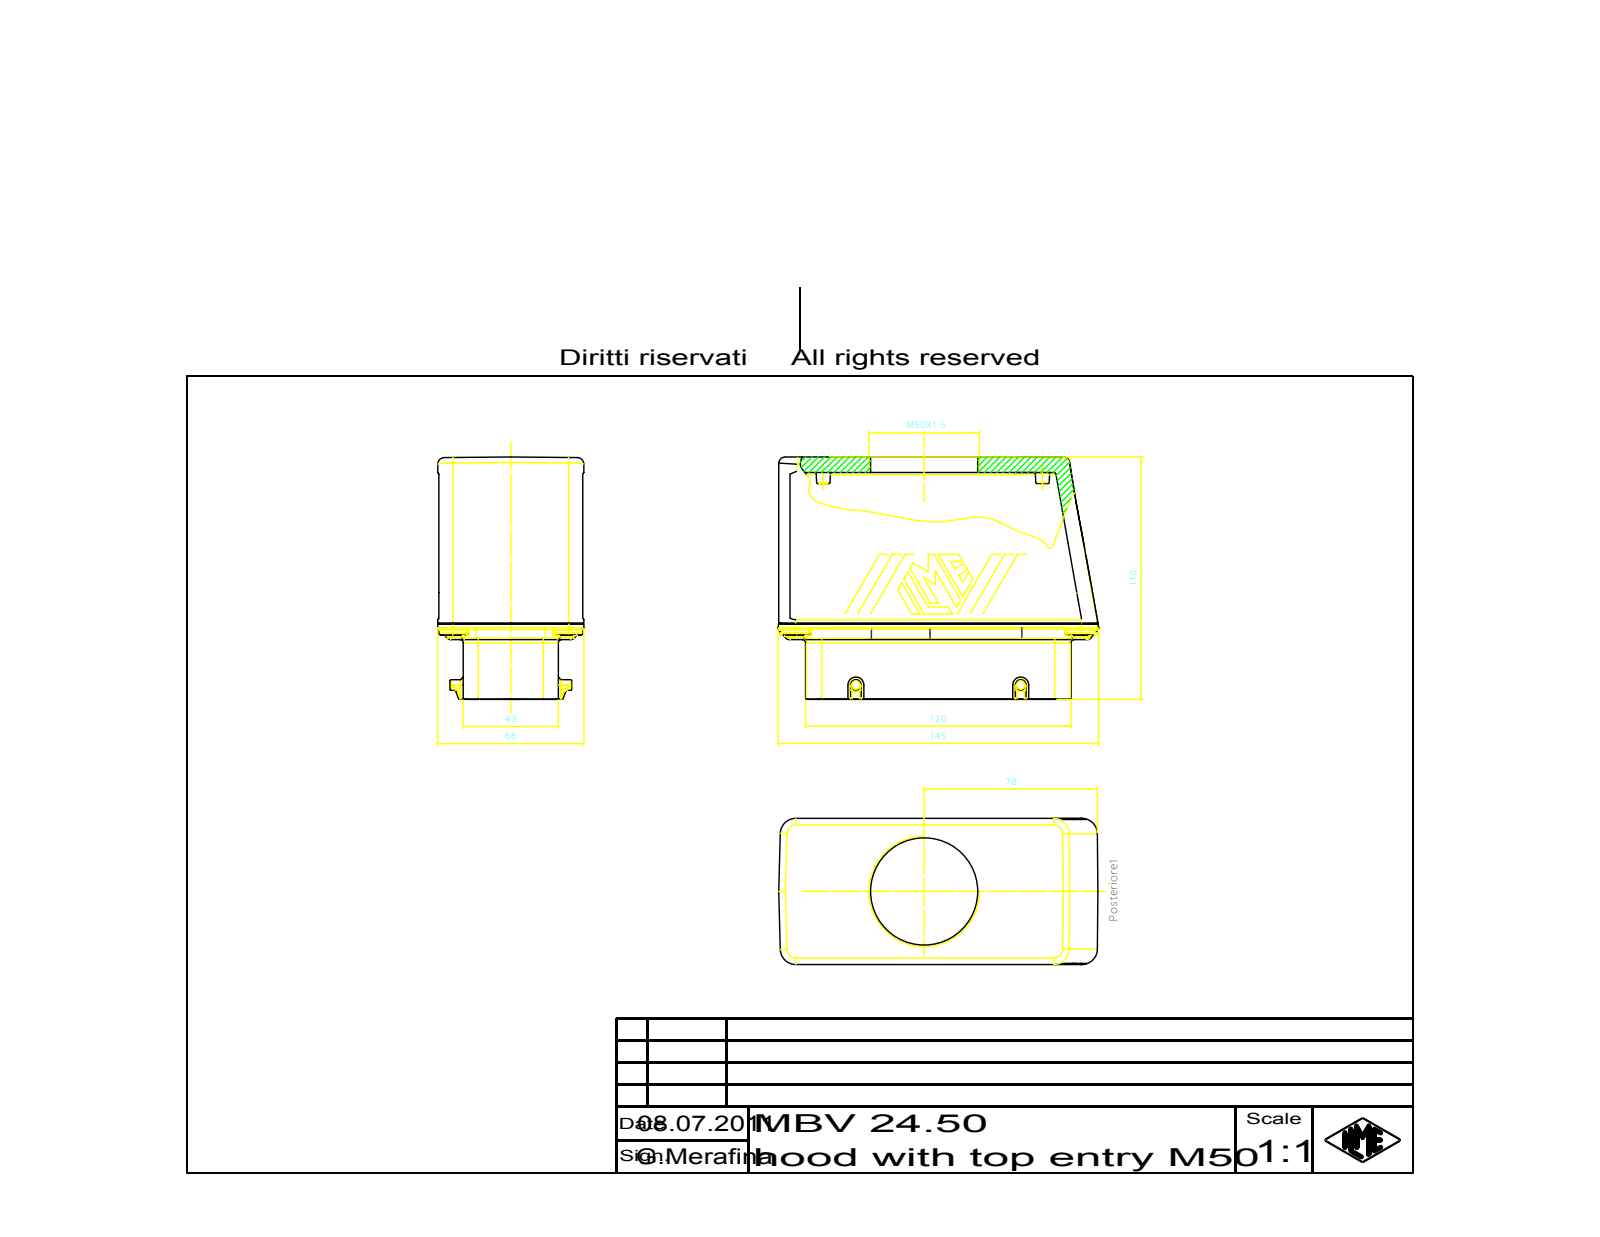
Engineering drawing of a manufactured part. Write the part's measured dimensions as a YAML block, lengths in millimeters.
part_name: "53848"
step_written_by: "CoCreate Modeling 16.00A 16-Aug-2008 (C) Parametric Technology GmbH (AUTOMOTIVE_DESIGN)"
units: millimeters
bodies: {solids: 1, faces: 690, planar: 376, cylindrical: 124, other: 190}
overall_size: [143.75, 108.97, 66.01]
volume: 698249
surface_area: 72306
round_holes:
  - {diameter: 50, count: 1}
round_bosses_or_shafts:
  - {diameter: 4.8, count: 2}
partial_cylinders:
  - {radius: 1, count: 44}
  - {radius: 7, count: 12}
  - {radius: 0.5, count: 8}
  - {radius: 0.3, count: 6}
  - {radius: 1.5, count: 6}
  - {radius: 3, count: 6}
  - {radius: 4.2, count: 4}
  - {radius: 5, count: 4}
face_to_face_distances: [65.01, 82.21, 0.4, 65.41, 11, 54.01, 54, 43, 11.01, 54.41]
